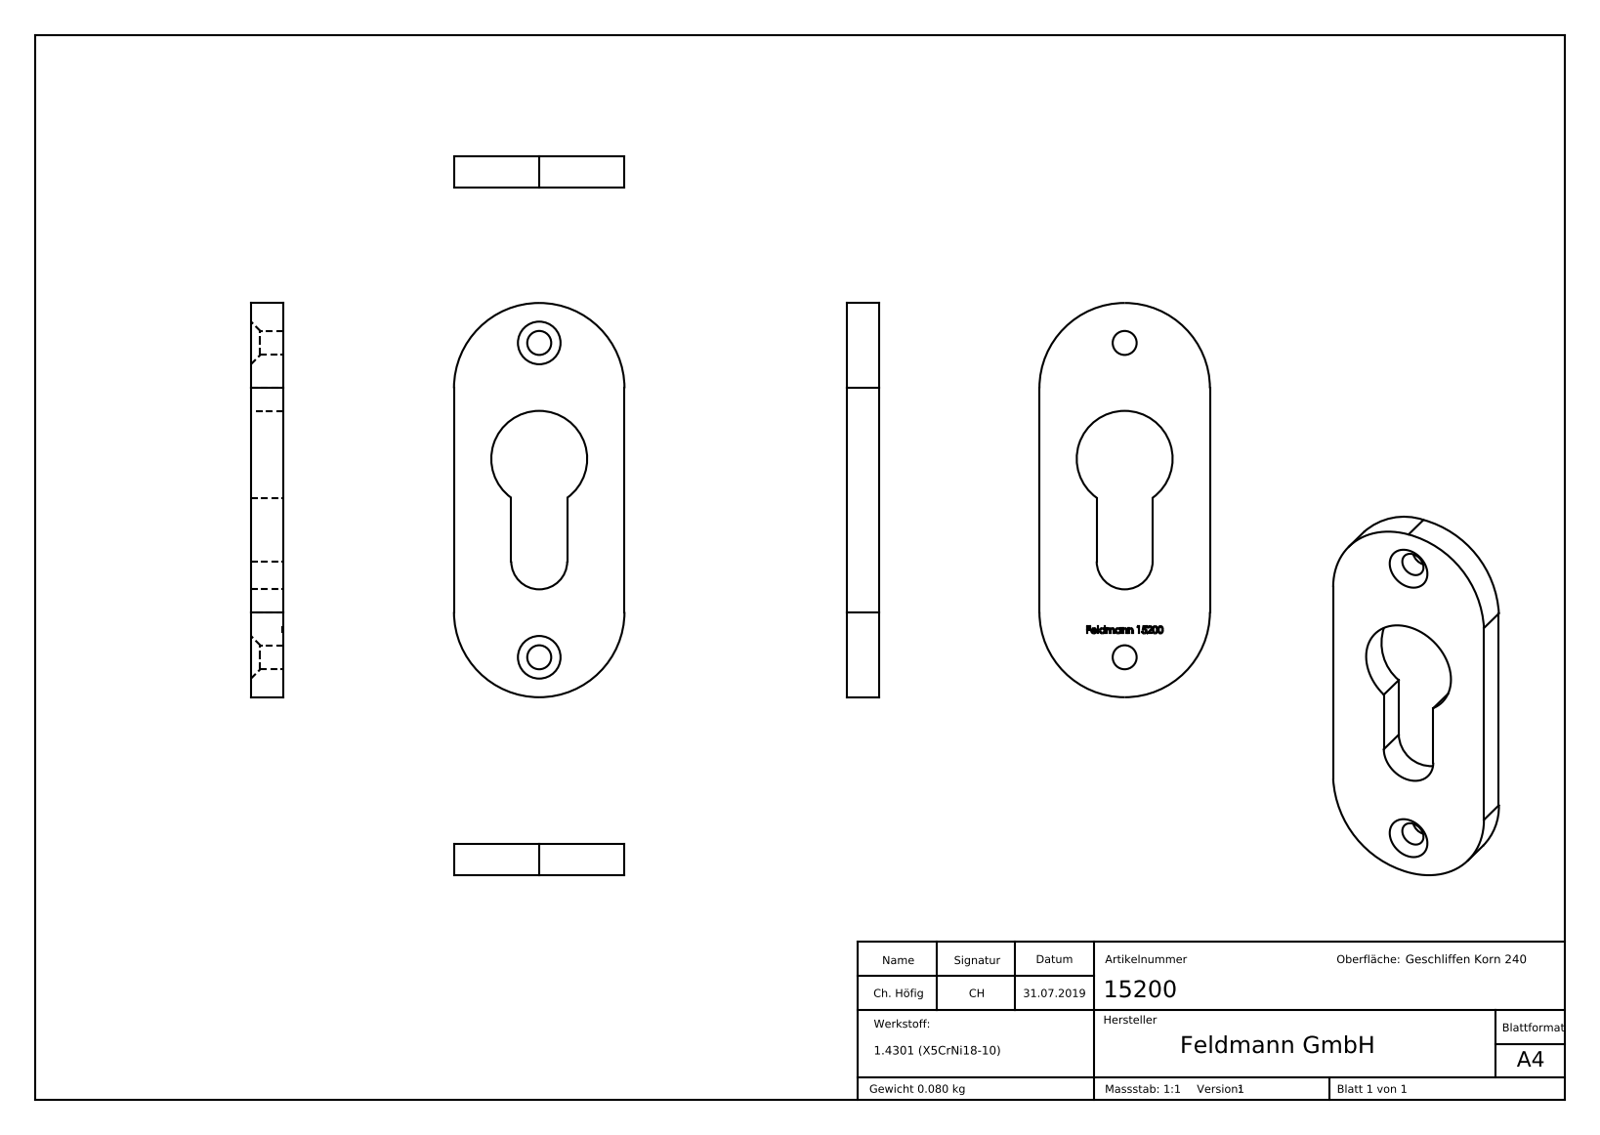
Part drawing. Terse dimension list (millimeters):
name: 15200
written by: SolidWorks 2015 (CONFIG_CONTROL_DESIGN)
unit: mm
bodies: 1 solid, 192 faces (96 planar, 12 cylindrical, 84 other)
size: 74 × 32 × 6
volume: 10 177 mm³; area: 5 188 mm²
holes: 2× ⌀4.5, 1× ⌀18
rounds: 2× R16, 1× R5.25
face distances: 6, 32, 10.75, 21.25, 10.5, 5.9, 2.97, 1.83, 0.39, 7.68
hole spacings: 21.75, 37.25, 59
